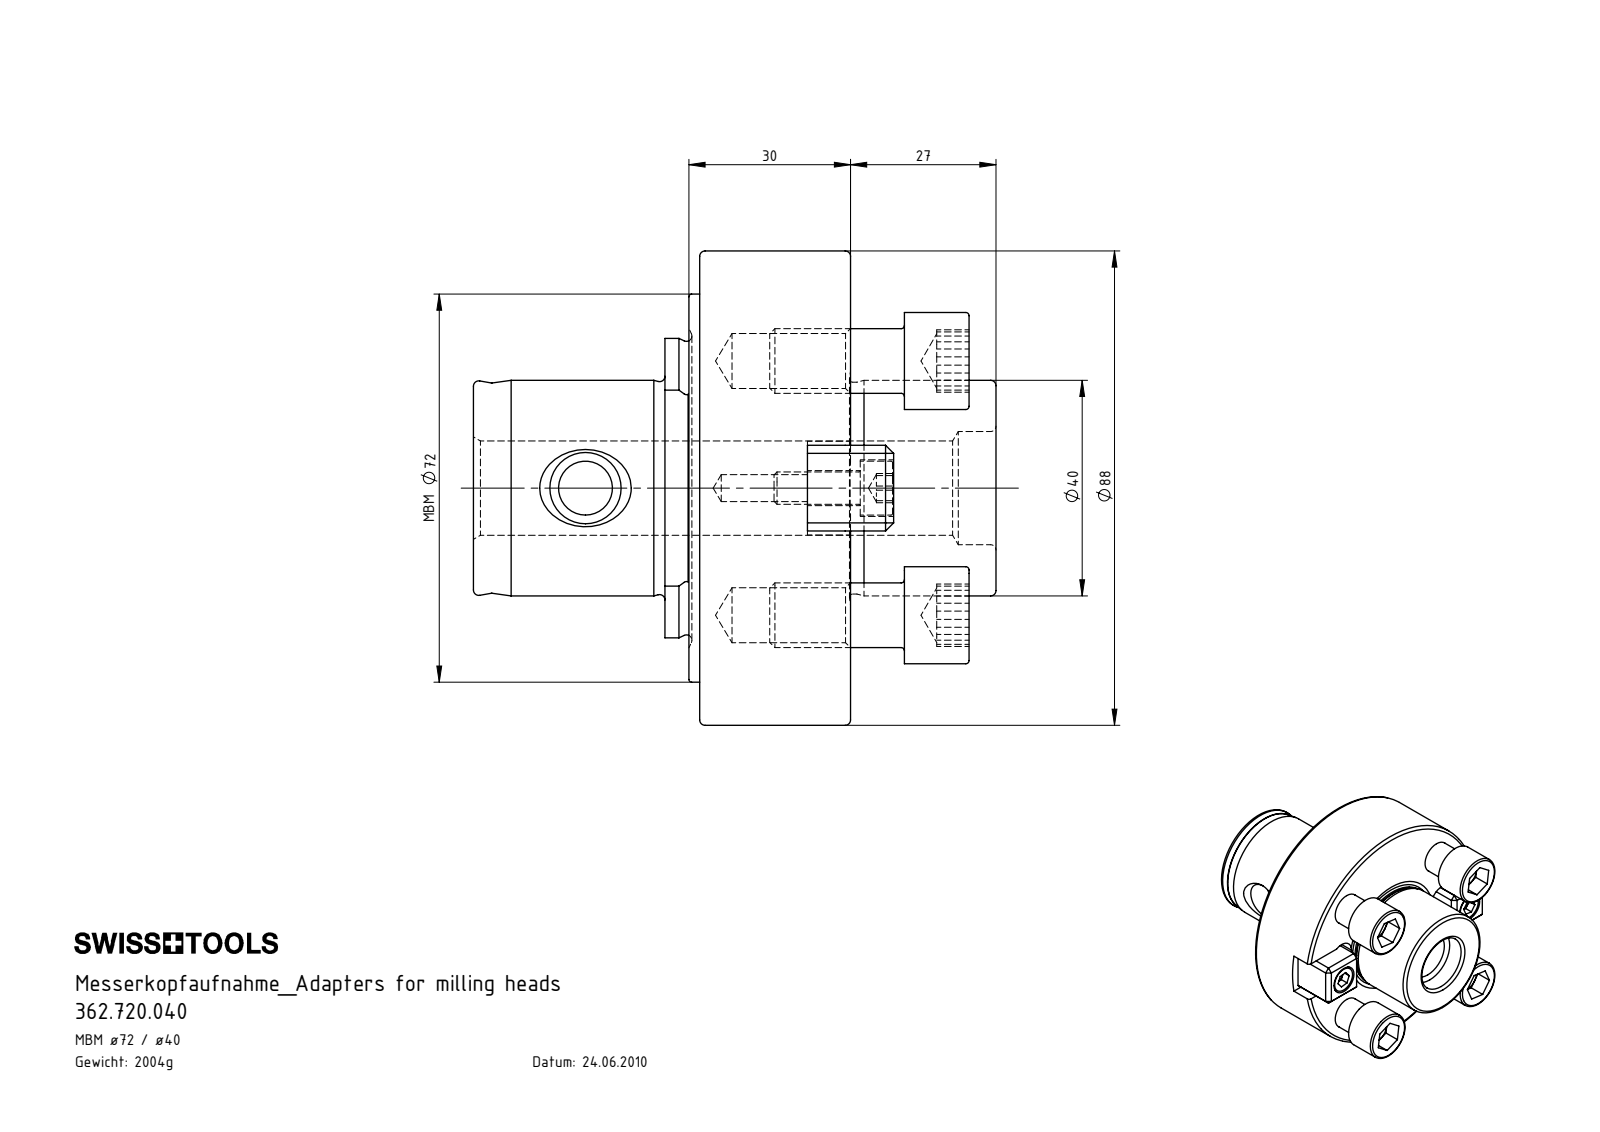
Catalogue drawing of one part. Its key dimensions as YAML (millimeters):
part_name: "MB7-D40.002.030_A; MB7.D40.002.030; ISO 4762 - M12 x 25_PreviewCfg; Ko1-ER1.001.016_A (+1 more)"
step_written_by: "SolidWorks 2017 (AUTOMOTIVE_DESIGN)"
units: millimeters
bodies: {solids: 9, faces: 241, planar: 147, cylindrical: 36, other: 58}
overall_size: [97, 88, 88]
volume: 255221
surface_area: 51804
round_holes:
  - {diameter: 10.2, count: 4}
  - {diameter: 5, count: 2}
  - {diameter: 6.5, count: 2}
  - {diameter: 10.5, count: 2}
  - {diameter: 10, count: 1}
  - {diameter: 17.5, count: 1}
  - {diameter: 21, count: 1}
round_bosses_or_shafts:
  - {diameter: 18, count: 4}
  - {diameter: 12, count: 4}
  - {diameter: 10, count: 2}
  - {diameter: 6, count: 2}
  - {diameter: 88, count: 1}
  - {diameter: 72, count: 1}
  - {diameter: 40, count: 1}
  - {diameter: 39.3, count: 1}
partial_cylinders:
  - {radius: 5.2, count: 4}
  - {radius: 27.77, count: 1}
face_to_face_distances: [28, 30, 22, 2, 42, 8, 40, 20, 55, 62]
hole_center_spacings: [25.39, 33.35, 47.16, 61.3, 33, 66.69, 66]
